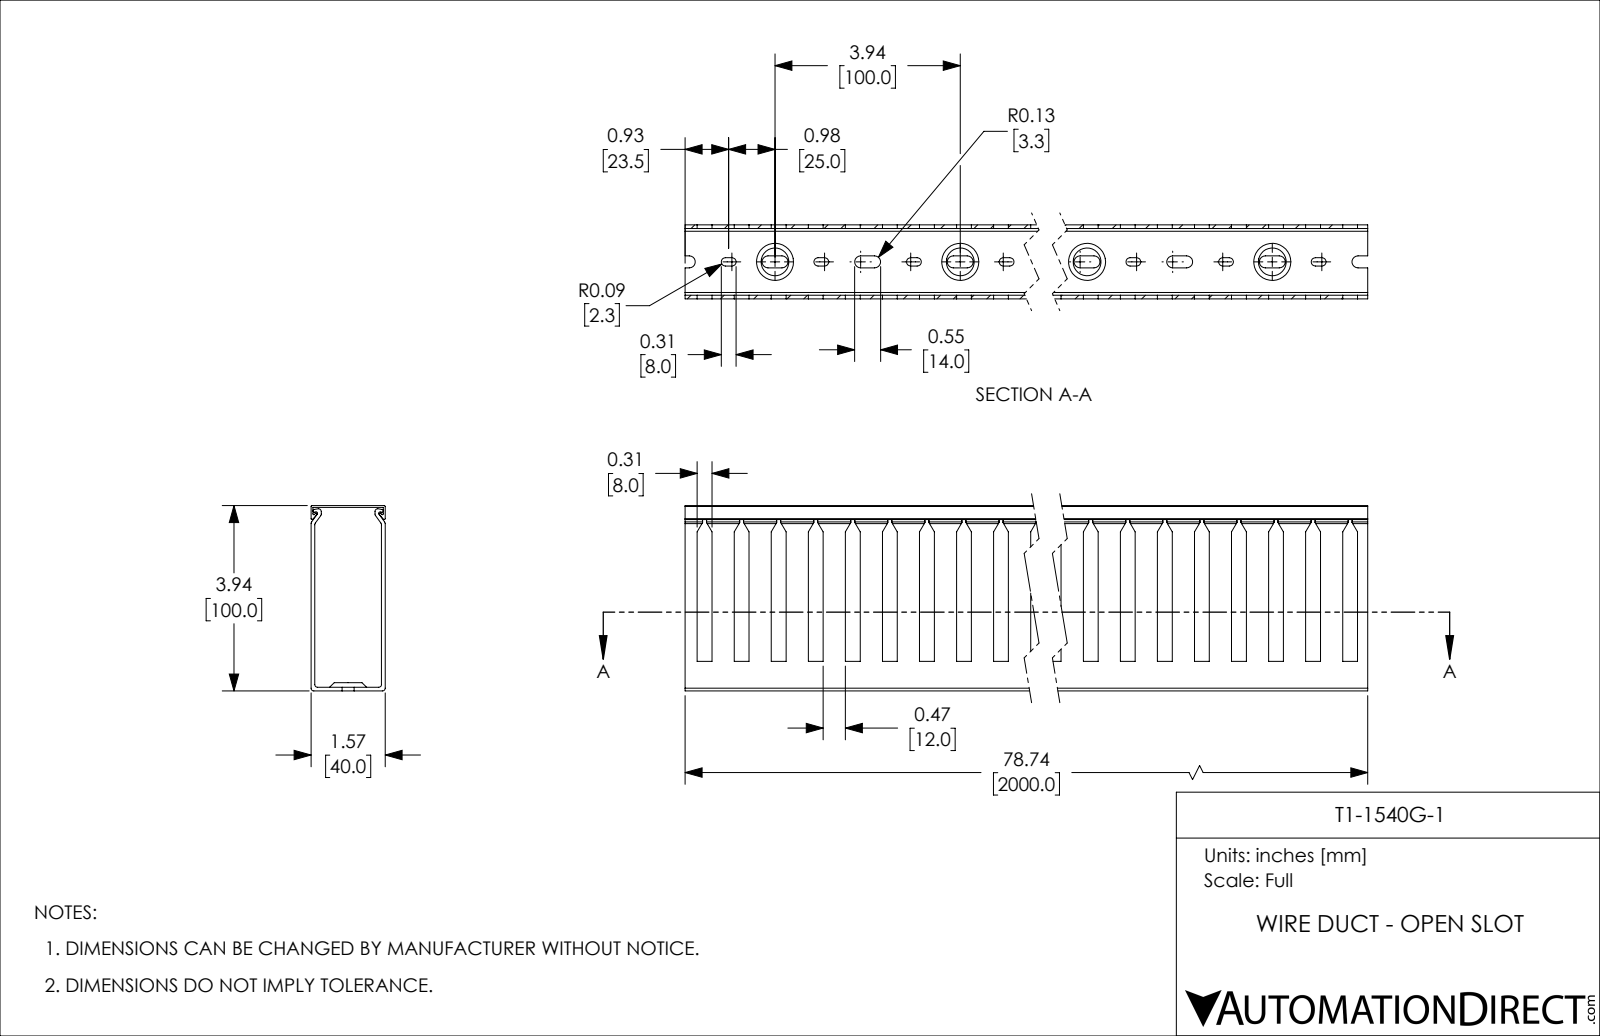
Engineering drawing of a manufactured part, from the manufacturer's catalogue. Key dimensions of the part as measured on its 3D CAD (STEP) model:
Part name (STEP PRODUCT): T1-1540W-1
STEP written by: SolidWorks 2021 (CONFIG_CONTROL_DESIGN)
Units: millimetres
Bodies: 2 solids, 1005 faces (534 planar, 431 cylindrical, 40 other)
Overall size (bounding box): 2000 × 100 × 40
Volume: 1 044 000 mm³ · Surface area: 1 164 000 mm²
Partial cylindrical surfaces — rounded edges, fillets, slot ends (radius × count): R2.25 ×80, R3.25 ×80, R1.5 ×12, R0.5 ×8, R0.75 ×6
Main face-to-face distances: 2, 38, 40, 36, 1, 100, 99, 97, 98, 39
